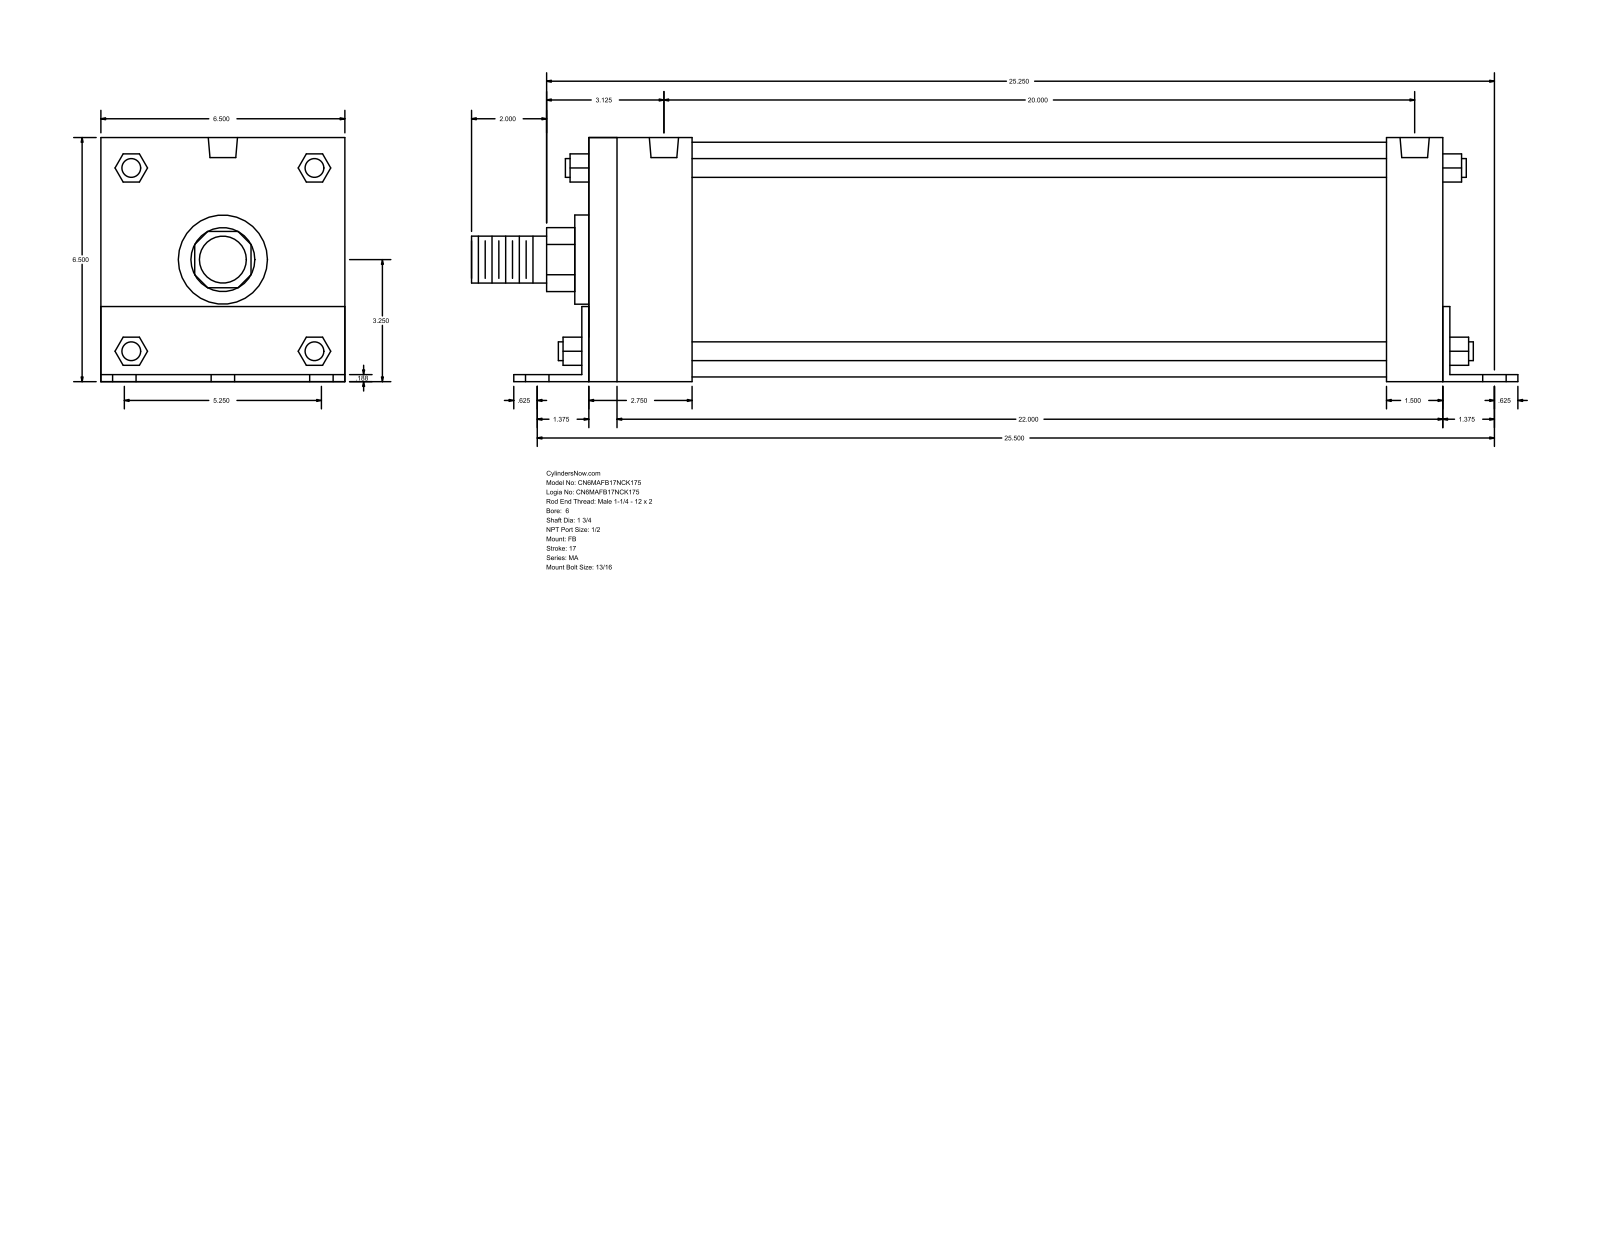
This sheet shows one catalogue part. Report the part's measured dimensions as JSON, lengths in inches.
{"part_name": "MA_FB__0600_1.75", "step_written_by": "GSSL Pune (CONFIG_CONTROL_DESIGN)", "units": "inches", "bodies": {"solids": 0, "faces": 140, "planar": 105, "cylindrical": 35, "other": 0}, "overall_size": [27.875, 6.502, 6.5], "round_holes": [[0.813, 6], [0.687, 4], [0.778, 2]], "round_bosses_or_shafts": [[0.5, 4], [6.25, 1], [2.375, 1], [1.75, 1], [1.25, 1]], "partial_cylinders_radius": [[0.852, 1], [1.262, 1]], "face_to_face_distances": [6.5, 0.187, 22.75, 6.502, 0.185, 6.315, 2.75, 2.937, 0.188, 22.938], "hole_center_spacings": [2.625, 25.635, 25.5, 3.377, 4.276, 5.25, 20, 22.28]}
